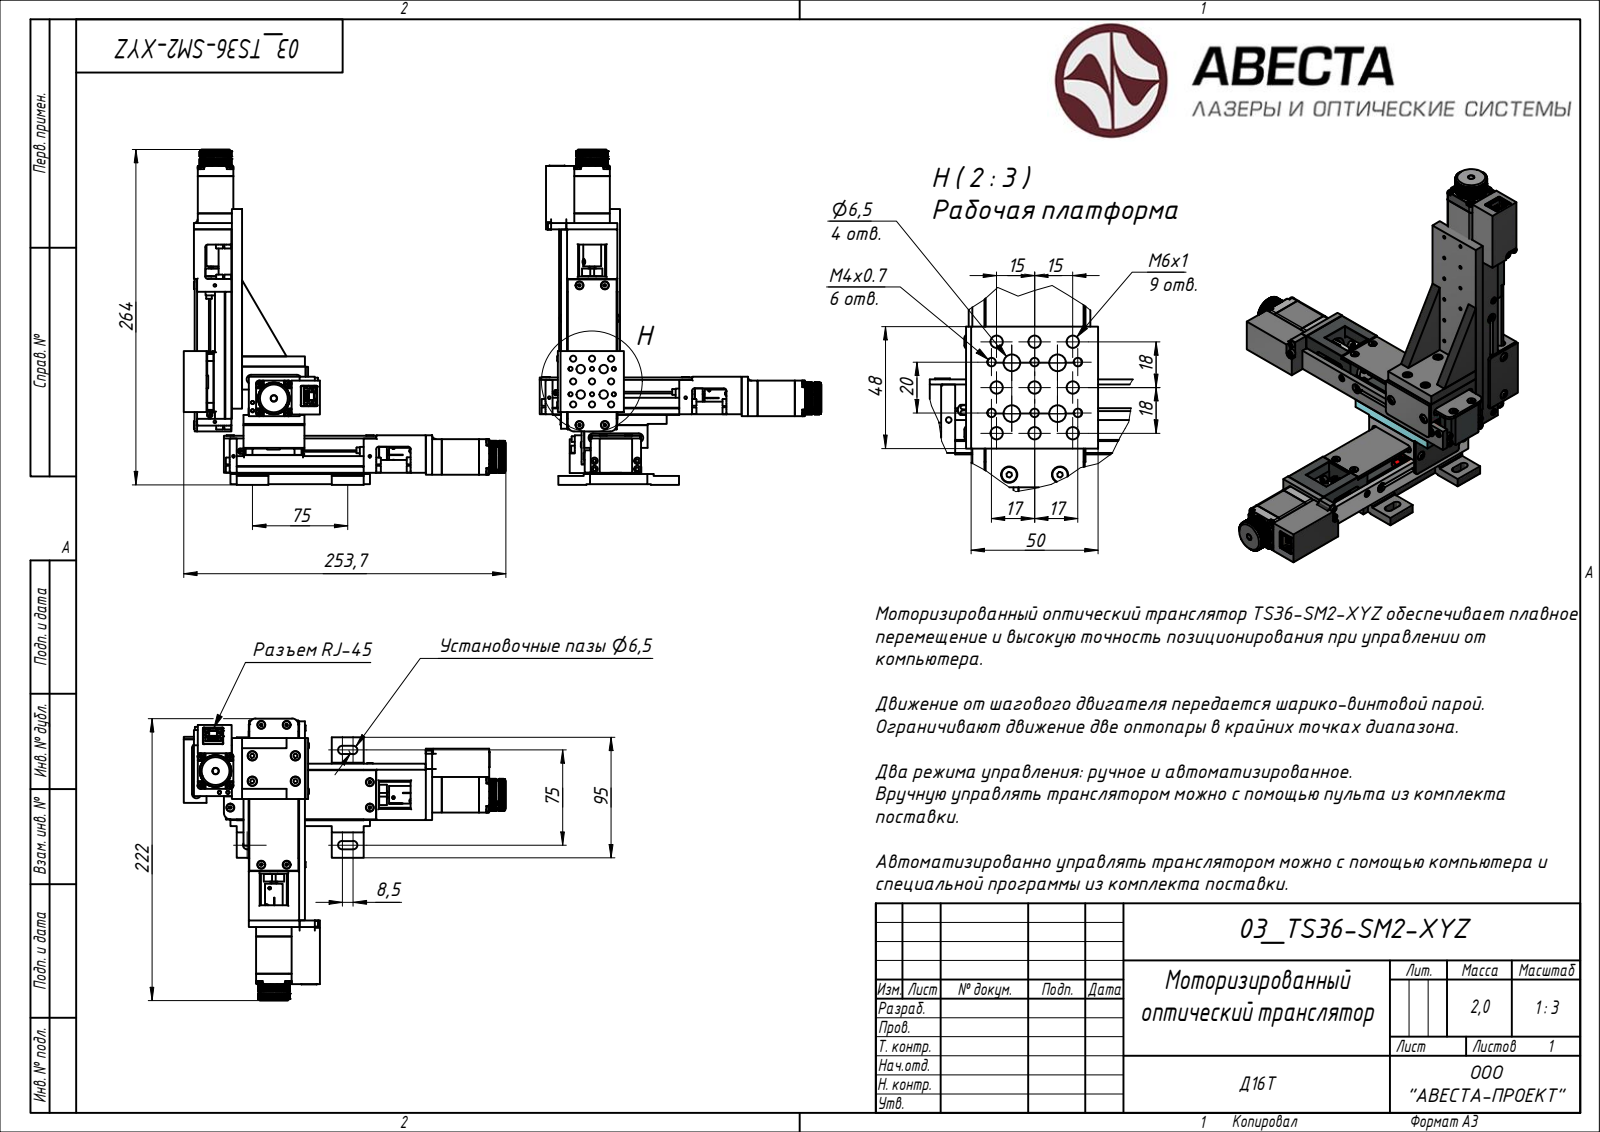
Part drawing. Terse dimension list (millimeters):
written by: Rhino 7.34 (AUTOMOTIVE_DESIGN)
unit: mm
bodies: 1 solid, 7084 faces (4303 planar, 1932 cylindrical, 849 other)
size: 264 × 253.7 × 222
volume: 757 826 mm³; area: 302 578 mm²
holes: 24× ⌀3.4, 24× ⌀6.5, 22× ⌀7.5, 21× ⌀3.24, 18× ⌀2.46, 15× ⌀1.05, 15× ⌀2.5, 12× ⌀3.8, 12× ⌀5, 9× ⌀2.15, 7× ⌀4.5, 6× ⌀2.46
bosses: 29× ⌀4.5, 19× ⌀3, 16× ⌀5.5, 15× ⌀6, 12× ⌀5.3, 10× ⌀2.5, 9× ⌀5, 6× ⌀7
rounds: 108× R0.5, 30× R2.5, 30× R3, 24× R2, 15× R2.46, 15× R2.46, 12× R1, 10× R1.23
face distances: 46, 0.5, 2.5, 2, 8, 29.5, 24.5, 4.5, 27.5, 27
hole spacings: 20, 18, 26.91, 1, 40, 60, 62.64, 10
